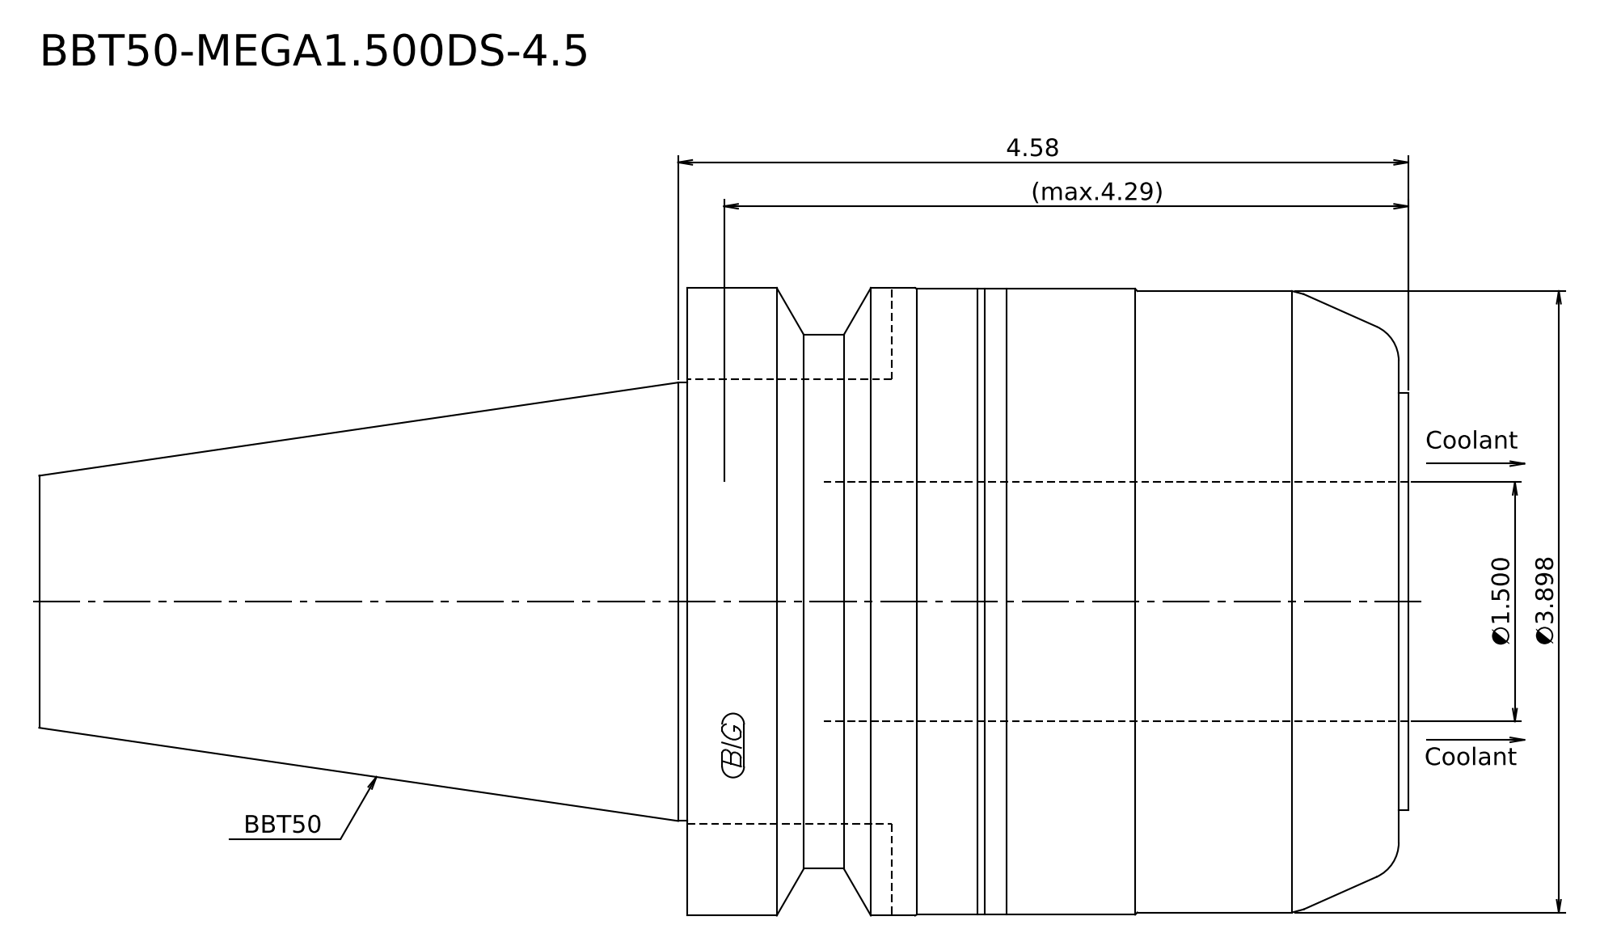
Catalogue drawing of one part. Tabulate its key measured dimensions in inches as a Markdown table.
| quantity | value |
| --- | --- |
| STEP written by | Kubotek KeyCreator 2011 V10.0.2 (22737) (automotive_design) |
| units | inches |
| bodies | 1 solid, 17 faces (4 planar, 7 cylindrical, 6 other) |
| overall size | 8.587 × 3.937 × 3.937 |
| volume | 67.07 in³ |
| surface area | 103.7 in² |
| round bosses / shafts (diameter × count) | 3.937 × 1, 3.925 × 1, 3.898 × 1, 3.346 × 1, 2.75 × 1, 2.618 × 1 |
| main face-to-face distances | 4.52, 0.059, 4.461, 8.587, 8.528, 4.067 |
